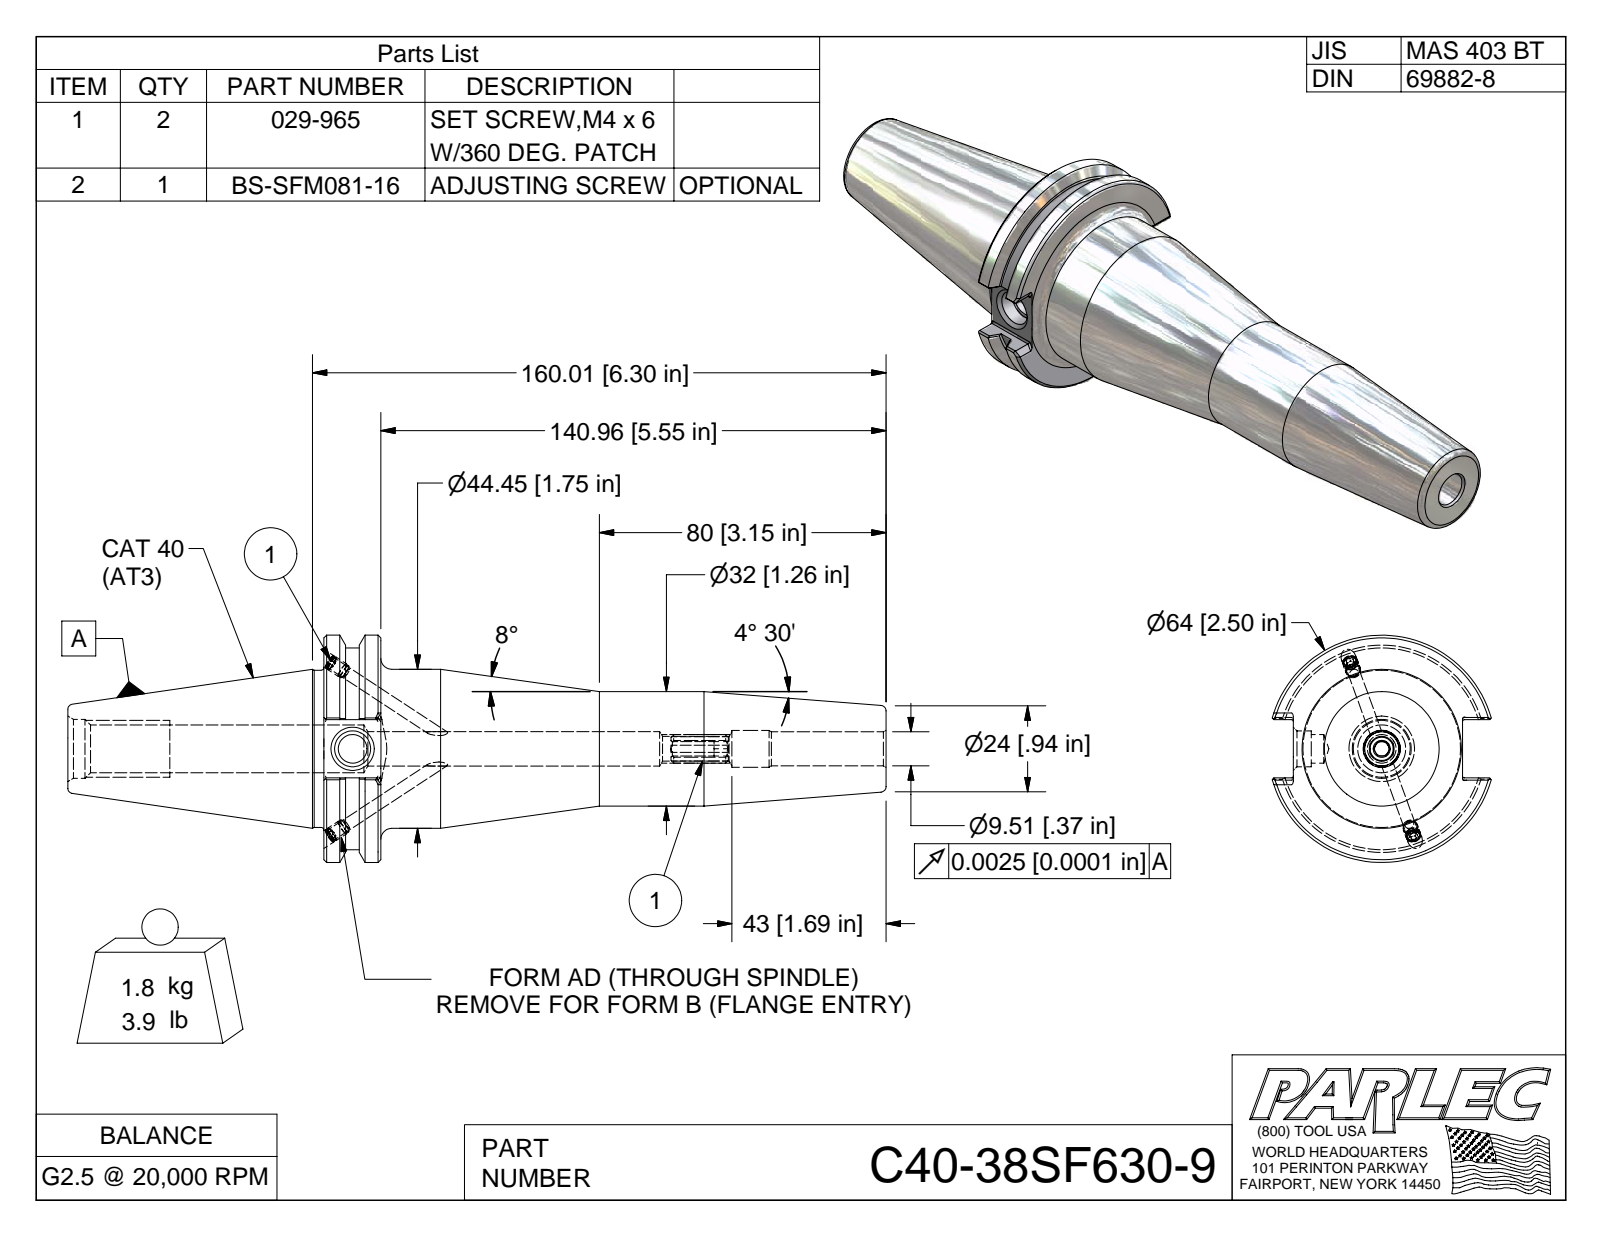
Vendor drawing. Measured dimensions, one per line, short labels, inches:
name: C40-38SF630-9; C40BC-38SF630-9-1; 029-965; BS-SFM081-16
written by: Autodesk Inventor 2009 (AUTOMOTIVE_DESIGN)
unit: in
bodies: 4 solids, 155 faces (66 planar, 35 cylindrical, 54 other)
size: 8.987 × 2.5 × 2.406
volume: 13.63 in³; area: 61.73 in²
holes: 2× ⌀0.13, 2× ⌀0.161, 1× ⌀0.374, 1× ⌀0.404
bosses: 2× ⌀0.165, 2× ⌀0.157, 1× ⌀2.5, 1× ⌀2.219, 1× ⌀1.75, 1× ⌀1.73, 1× ⌀1.26
rounds: 12× R0.02, 1× R0.157
face distances: 0.625, 6.175, 5.55, 0.64, 1.86, 2.812, 3.437, 8.987, 3.201, 0.389
